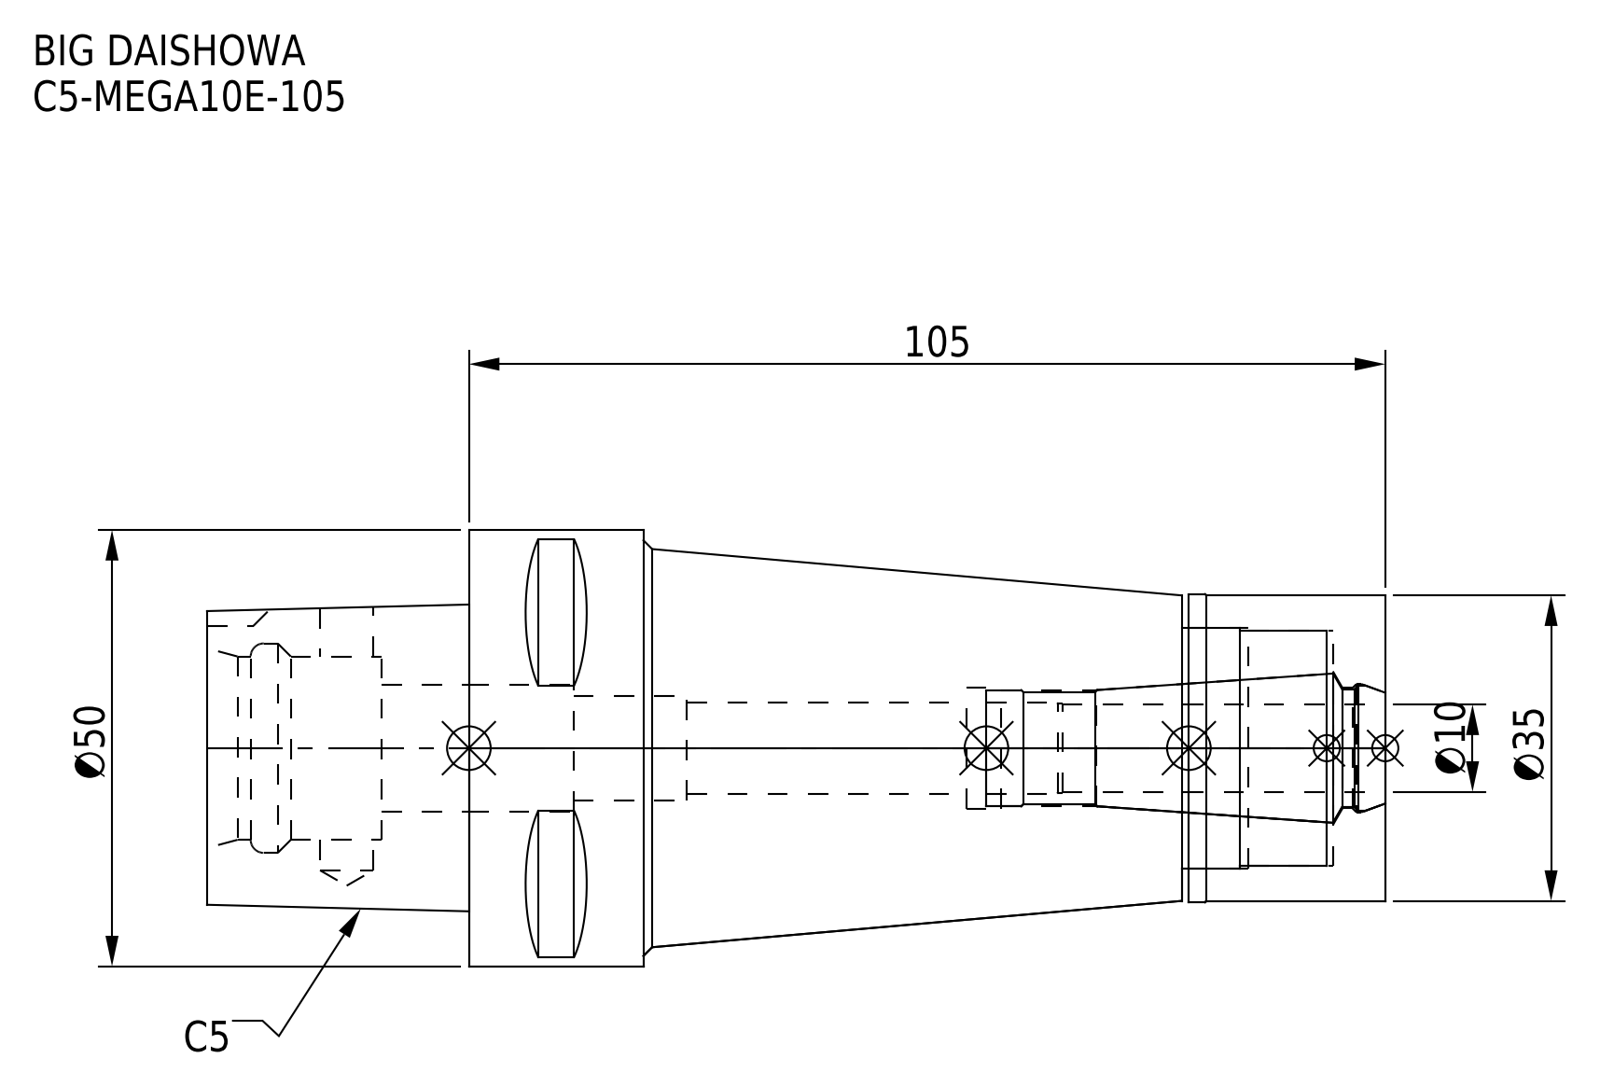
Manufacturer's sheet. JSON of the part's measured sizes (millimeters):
{"part_name": "C5-MEGA10E-105; MEN10_1.stp; C5-MEGA10E-105-100.stp; C5-MEGA10E-105-100-FreeParts (+3 more)", "step_written_by": "SolidWorks 2019 (CONFIG_CONTROL_DESIGN)", "units": "millimeters", "bodies": {"solids": 2, "faces": 100, "planar": 37, "cylindrical": 39, "other": 24}, "overall_size": [135, 50, 50], "volume_mm3": 143796, "surface_area_mm2": 30490, "round_holes": [[6.1, 1], [10.4, 1], [12, 1], [13.3, 1], [13.8, 1], [13.9, 1], [14.5, 1], [14.7, 1], [21, 1], [24, 1], [27, 1], [27.5, 1]], "round_bosses_or_shafts": [[50, 1], [35.3, 1], [35, 1]], "partial_cylinders_radius": [[4, 1]], "face_to_face_distances": [105, 30, 22.5, 82.5, 135, 112.5, 81.7, 23.3, 0.8, 111.7]}
